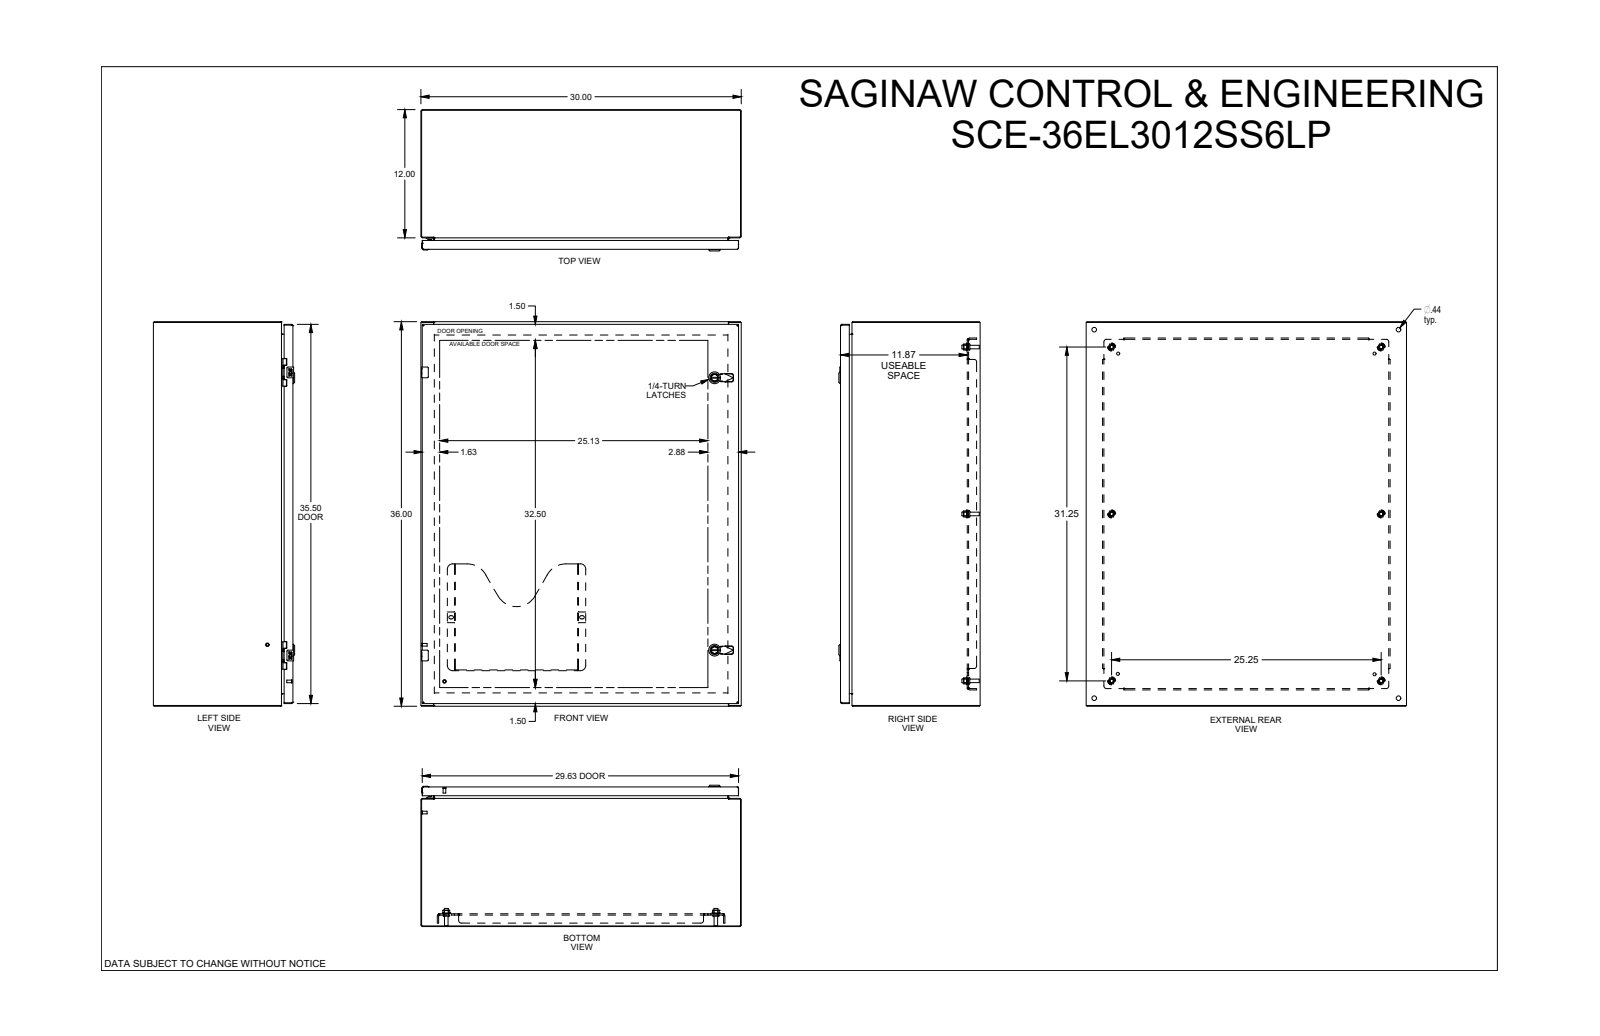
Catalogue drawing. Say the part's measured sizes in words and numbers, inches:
The part is named "SCE-36EL3012LP". Its 3-D file was written by "SolidWorks 2021 (AUTOMOTIVE_DESIGN)". It is 51 solids with 2989 faces: 1139 planar, 888 cylindrical and 962 other. Overall it measures 36 by 30 by 13.23 inches. Its volume is 447 cubic inches and its surface area 10 648 square inches. Round holes: 6 of diameter 0.367, 6 of diameter 0.5, 4 of diameter 0.172, 4 of diameter 0.205, 4 of diameter 0.244, 4 of diameter 0.266, 4 of diameter 0.281, 4 of diameter 0.375, 4 of diameter 0.437, 2 of diameter 0.04, 2 of diameter 0.188, 2 of diameter 0.197. Round bosses or shafts: 6 of diameter 0.366, 6 of diameter 0.332, 6 of diameter 0.17, 4 of diameter 0.25, 4 of diameter 0.248, 4 of diameter 0.24, 3 of diameter 0.196, 2 of diameter 1.102. Partial cylindrical surfaces (rounded edges, fillets, slot ends): 56 of radius 0.012, 40 of radius 0.01, 20 of radius 0.015, 20 of radius 0.02, 17 of radius 0.04, 13 of radius 0.06, 12 of radius 0.029, 12 of radius 0.1. The main face-to-face distances are 0.075, 0.06, 13.073, 12.998, 13.013, 12.938, 1.2, 11.873, 1, 0.125. The hole center spacings are 0.985, 15.625, 26.5, 32.915, 42.462, 30.638, 31.25, 0.02.
